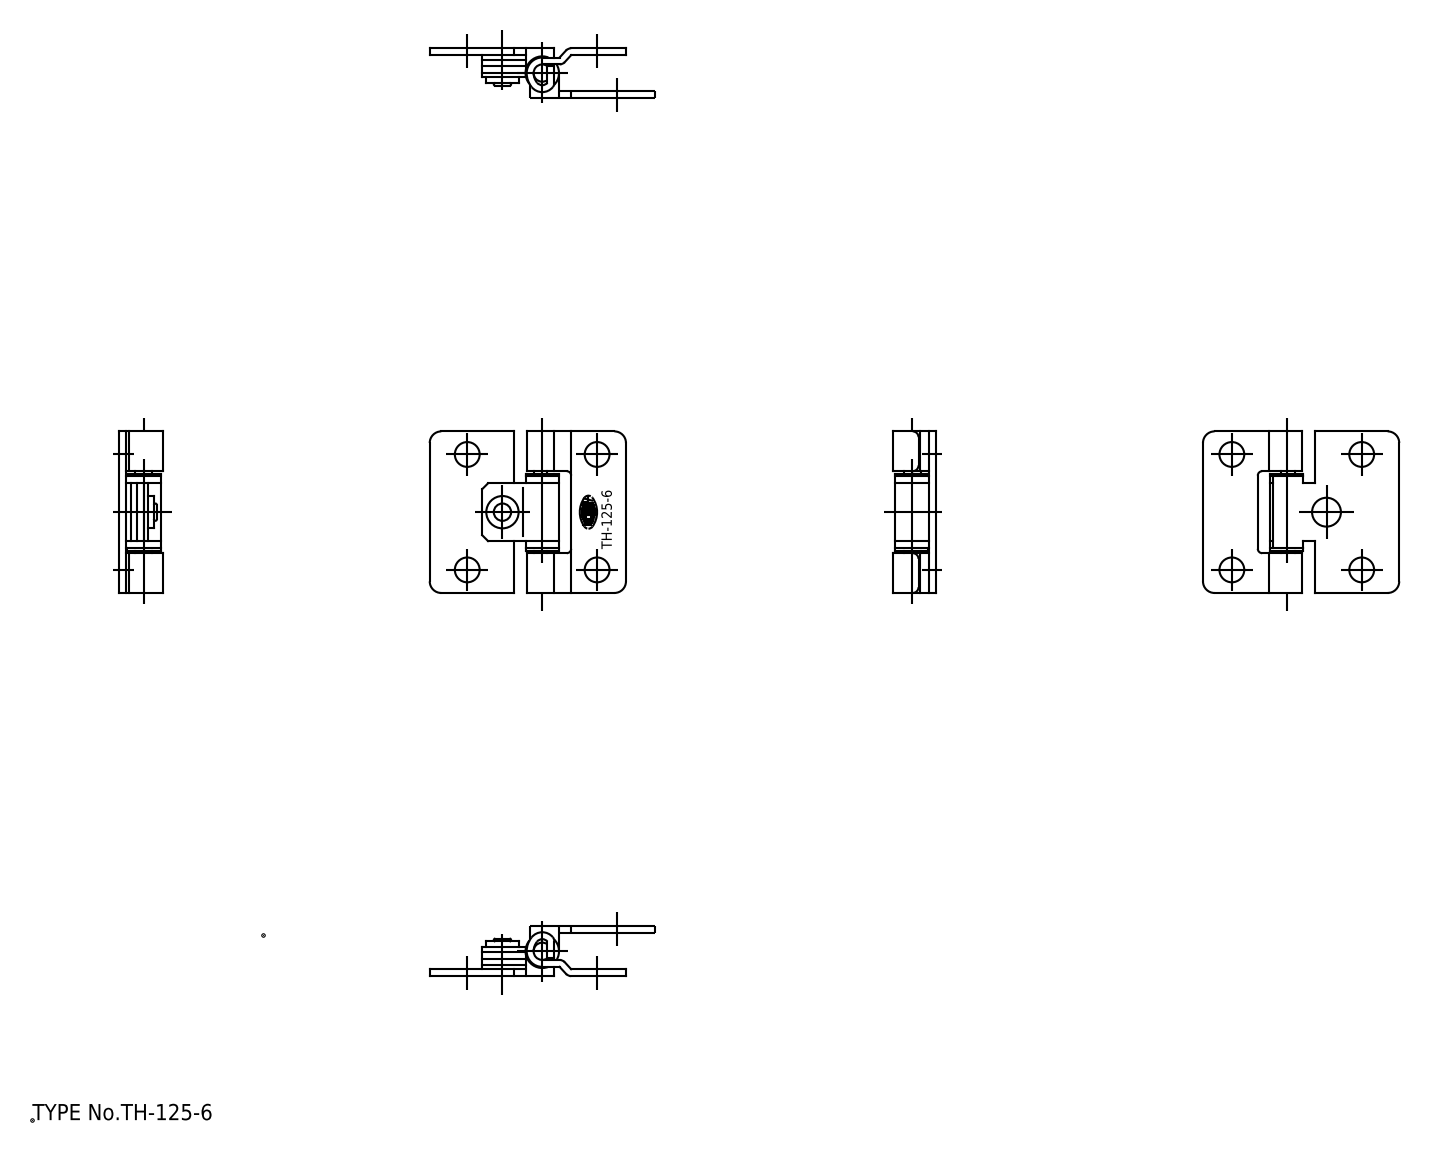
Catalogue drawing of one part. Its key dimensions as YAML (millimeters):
part_name: "washer_2; washer_1; shaft; rivet (+3 more)"
step_written_by: "spGate 19.8.4 (****-****-****-****) (AUTOMOTIVE_DESIGN)"
units: millimeters
bodies: {solids: 9, faces: 142, planar: 72, cylindrical: 66, other: 4}
overall_size: [34, 28, 7.6]
volume: 1906
surface_area: 4005
round_holes:
  - {diameter: 4.3, count: 4}
  - {diameter: 2.5, count: 1}
  - {diameter: 3, count: 1}
round_bosses_or_shafts:
  - {diameter: 5.8, count: 1}
  - {diameter: 5.6, count: 1}
partial_cylinders:
  - {radius: 2, count: 4}
  - {radius: 1.2, count: 3}
  - {radius: 0.75, count: 2}
  - {radius: 1, count: 2}
  - {radius: 1.17, count: 1}
  - {radius: 2.1, count: 1}
  - {radius: 2.35, count: 1}
  - {radius: 2.37, count: 1}
face_to_face_distances: [1.2, 0.8, 3, 2.2, 2, 4.2, 0.4, 9, 19, 3.8]
hole_center_spacings: [11.71, 19.21, 20, 22.5, 30.1]
